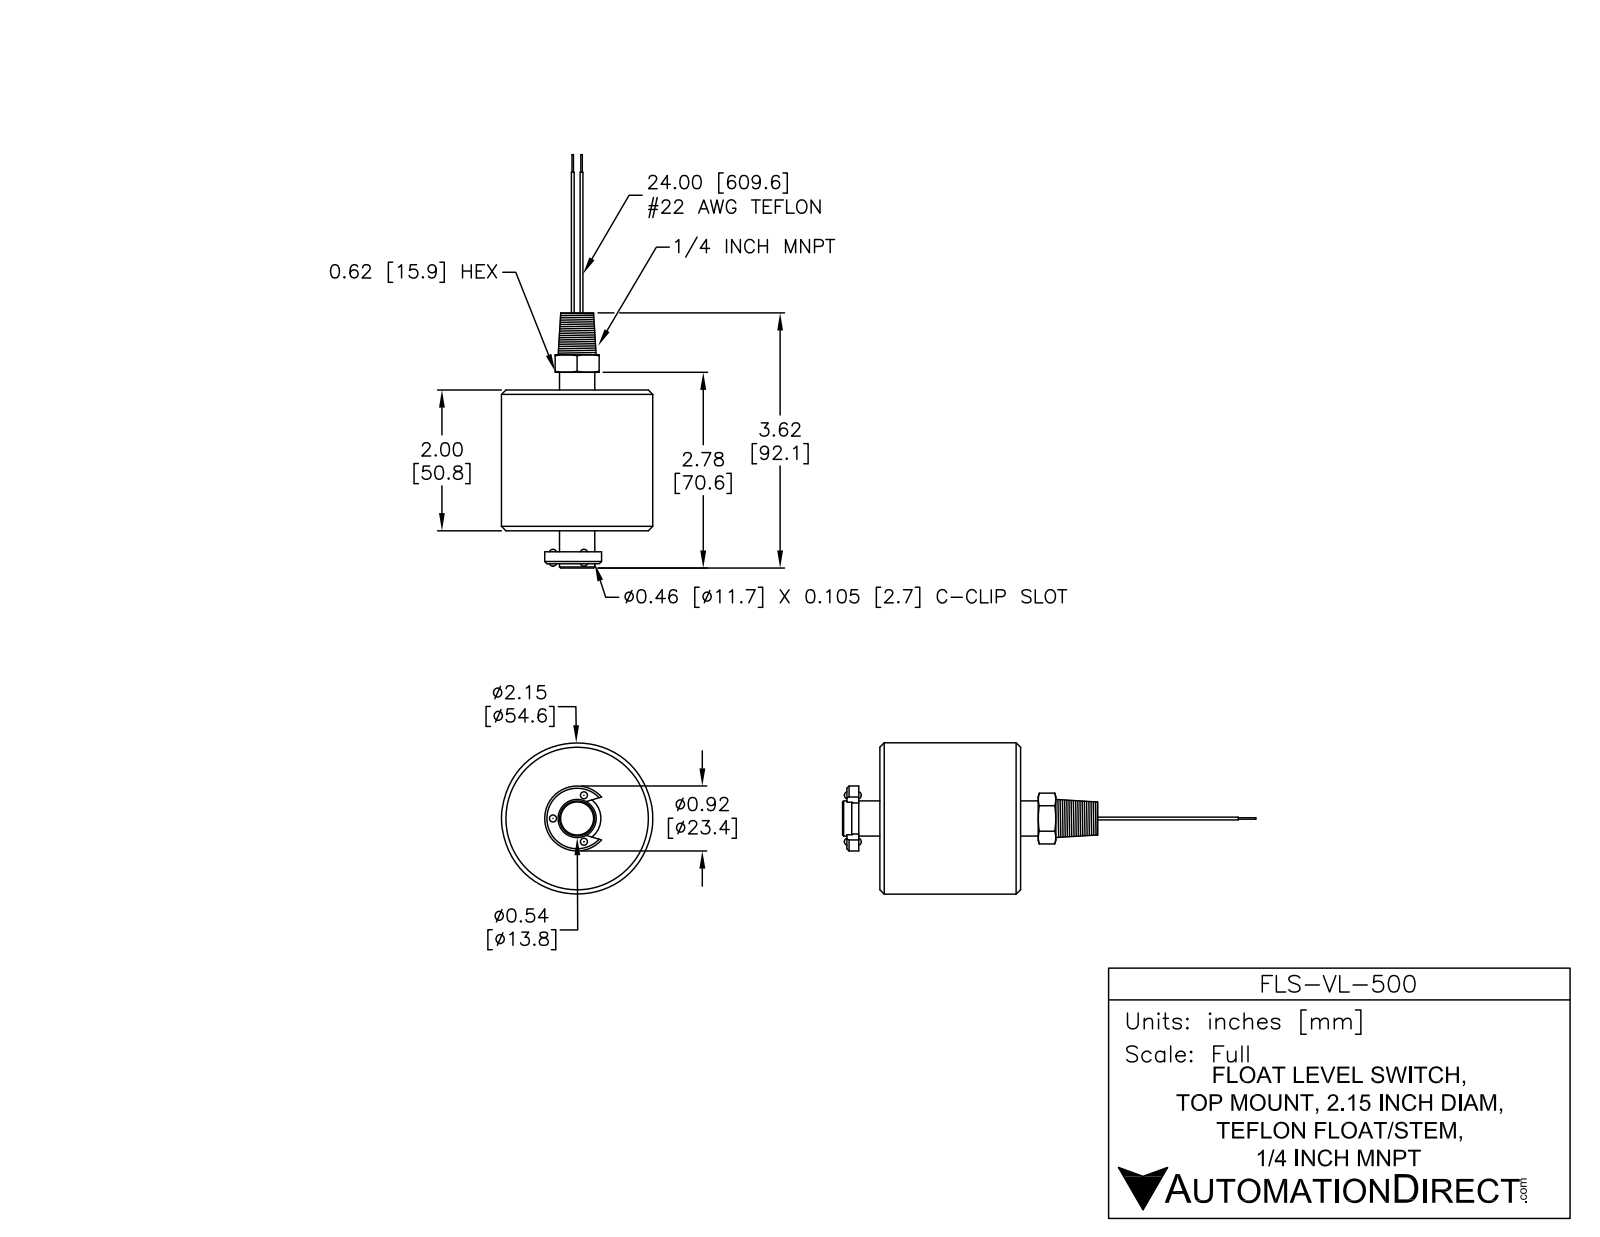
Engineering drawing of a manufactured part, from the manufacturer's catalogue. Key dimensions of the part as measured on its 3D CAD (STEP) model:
Part name (STEP PRODUCT): FLS-VL-500
STEP written by: SolidWorks 2013 (AUTOMOTIVE_DESIGN)
Units: inches
Bodies: 6 solids, 124 faces (36 planar, 56 cylindrical, 32 other)
Overall size (bounding box): 6.199 × 2.15 × 2.15
Volume: 2.02 in³ · Surface area: 59.09 in²
Round holes (diameter × count): ⌀0.1 ×3, ⌀0.46 ×1, ⌀0.55 ×1, ⌀2.04 ×1
Round bosses / shafts (diameter × count): ⌀0.04 ×4, ⌀0.02 ×2, ⌀2.15 ×1, ⌀1 ×1, ⌀0.875 ×1, ⌀0.813 ×1, ⌀0.5 ×1
Partial cylindrical surfaces — rounded edges, fillets, slot ends (radius × count): R0.229 ×1, R0.461 ×1
Main face-to-face distances: 0.055, 1.915, 1.97, 1.86, 0.143, 0.197, 2.057, 2.112, 0.095, 0.148
Hole centre spacings: 0.344, 0.55, 0.66
